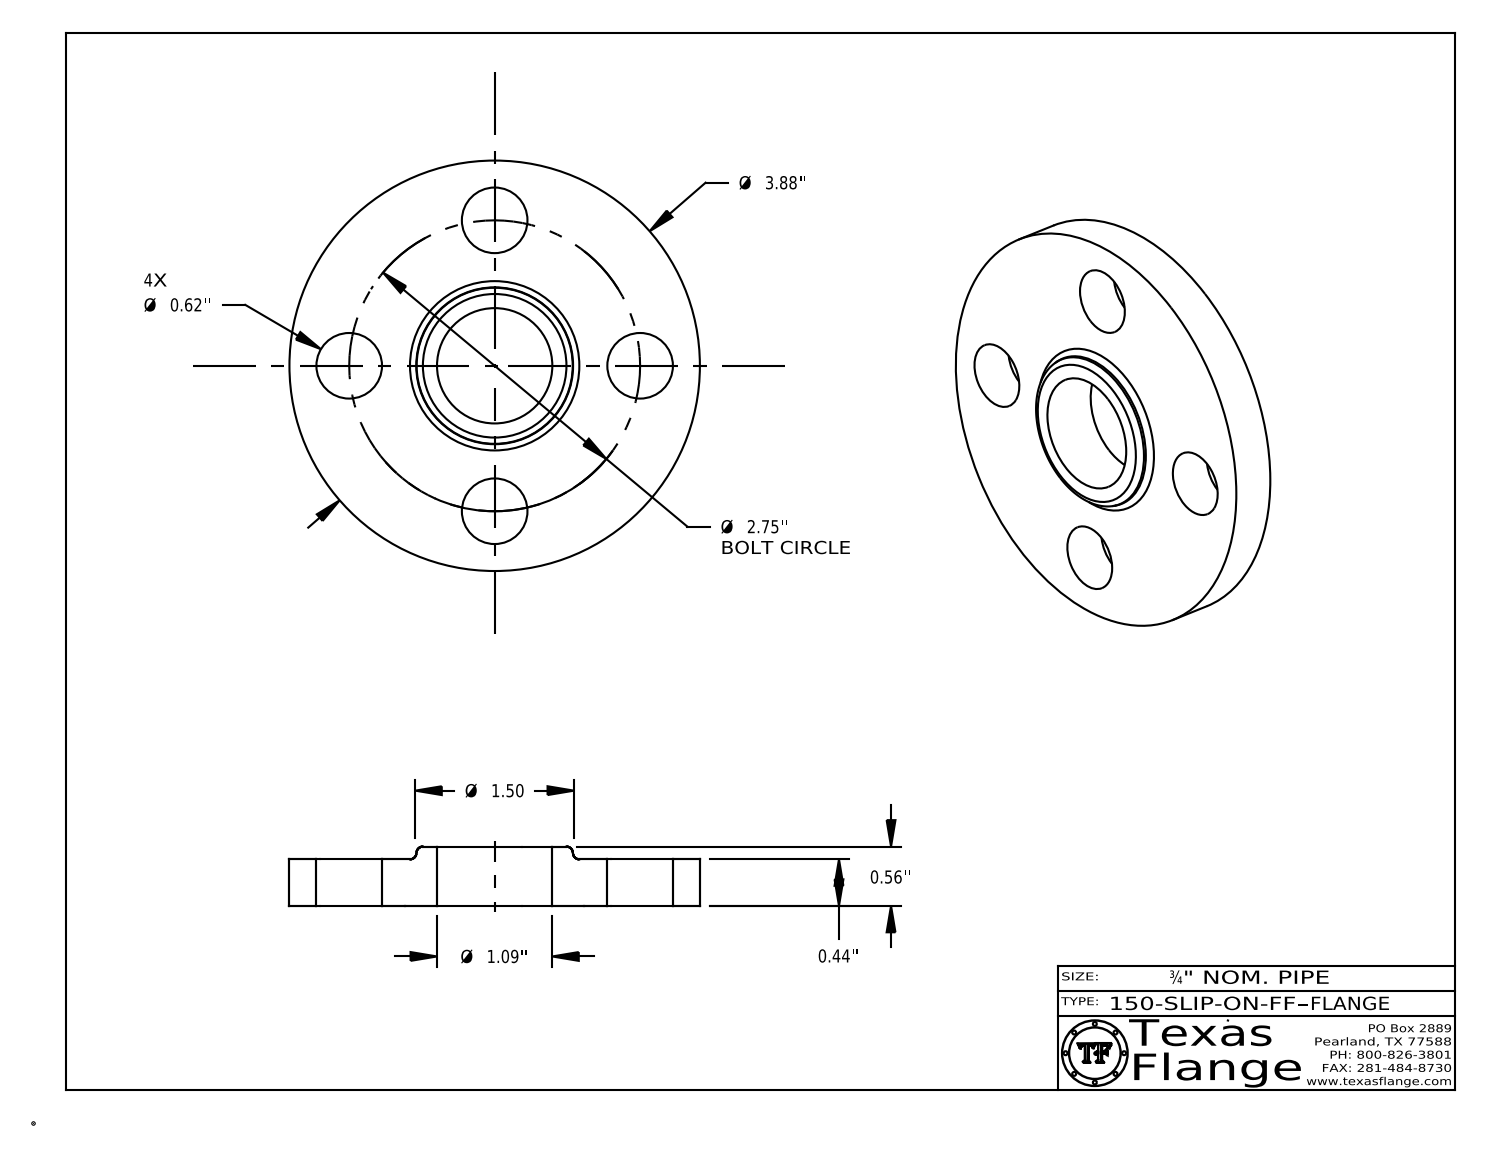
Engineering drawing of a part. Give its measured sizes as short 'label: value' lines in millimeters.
name: 150-SLIP-ON-FF
written by: CATIA V5 STEP AP214 (AUTOMOTIVE_DESIGN)
unit: mm
bodies: 1 solid, 407 faces (369 planar, 32 cylindrical, 6 other)
size: 98.6 × 98.6 × 14.2
volume: 71 350 mm³; area: 19 660 mm²
holes: 4× ⌀15.7, 1× ⌀12.6, 1× ⌀27.7
bosses: 8× ⌀0.8, 1× ⌀98.6, 1× ⌀9.9
face distances: 11.2, 14.2, 3, 10.8, 0.4, 3.4, 3.8, 3.7, 0.7, 3.1
hole spacings: 34.9, 49.4, 26.7, 64.5, 69.9
